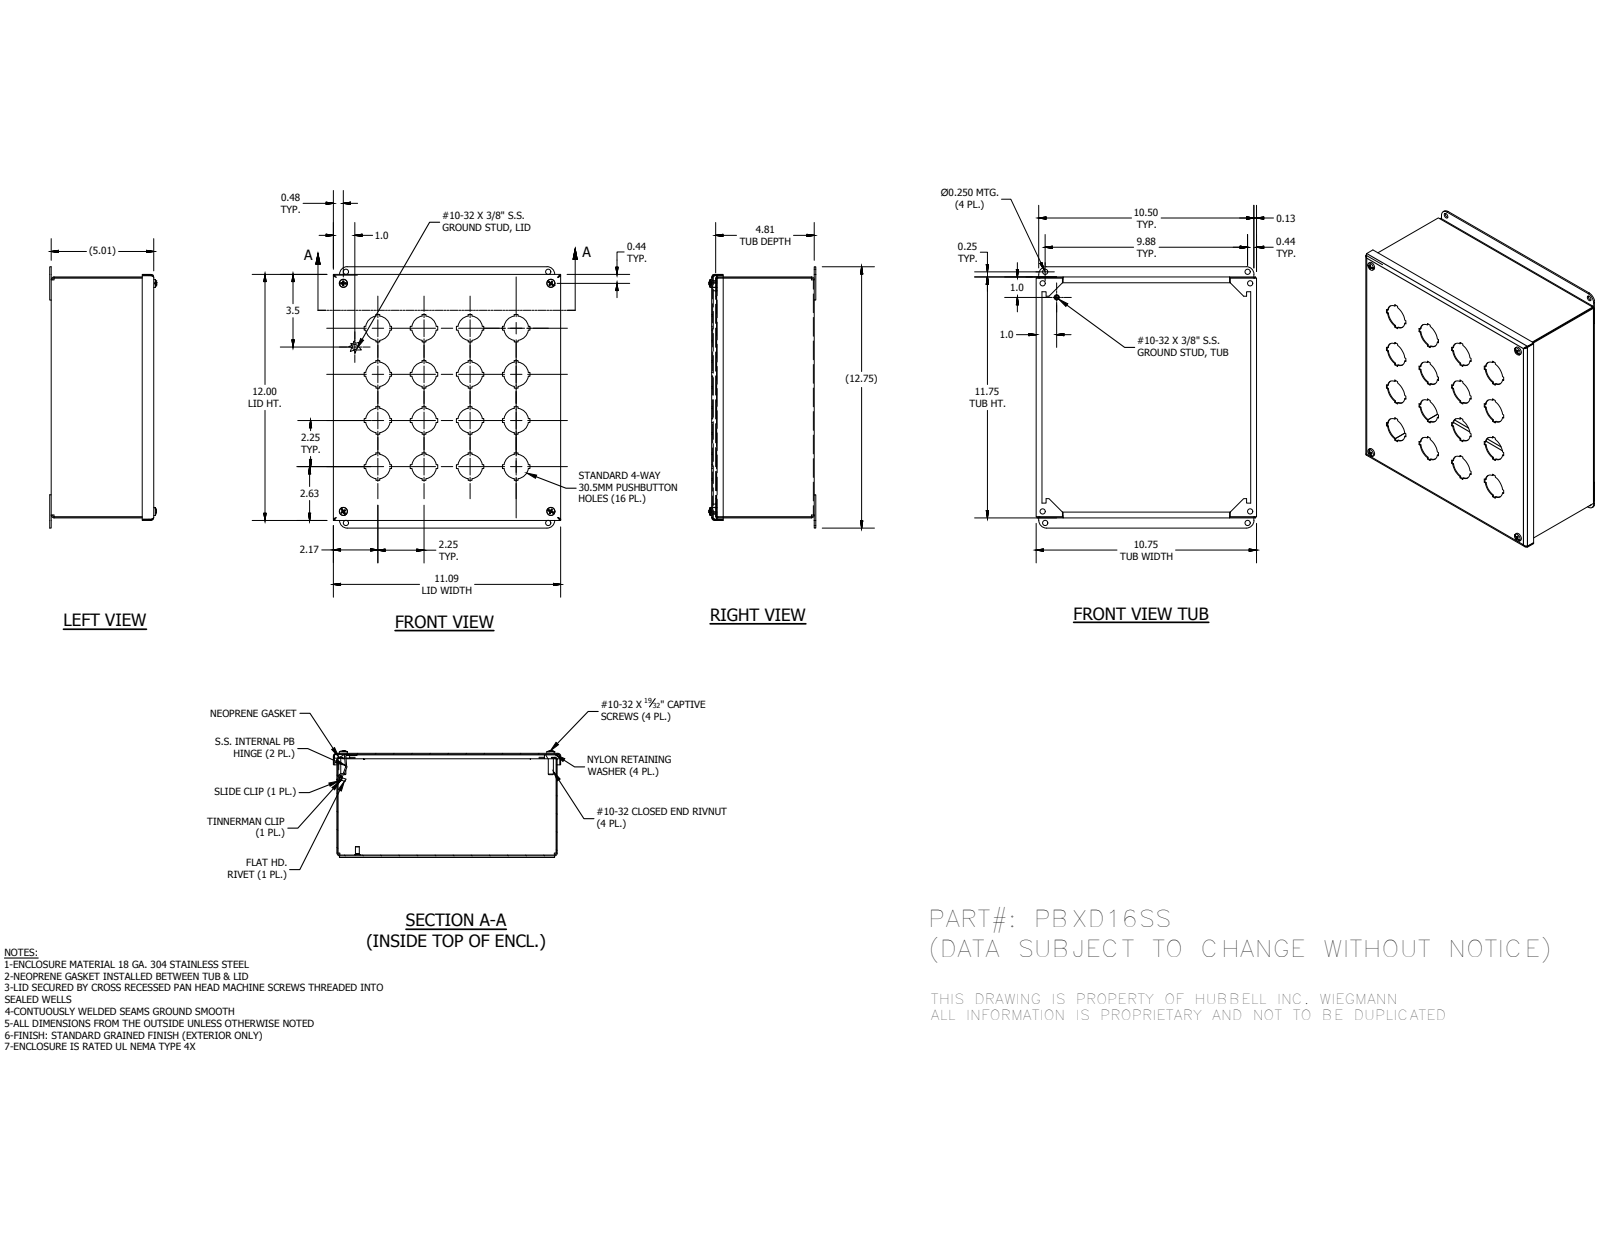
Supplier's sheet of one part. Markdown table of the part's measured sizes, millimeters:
| quantity | value |
| --- | --- |
| part name | PBXD16SSLID; 37210; 39077; PBXD16SSBKP (+8 more) |
| STEP written by | Autodesk Inventor 2016 (AUTOMOTIVE_DESIGN) |
| units | millimeters |
| bodies | 25 solids, 905 faces (601 planar, 196 cylindrical, 108 other) |
| overall size | 323.85 × 281.78 × 132.09 |
| volume | 504 523 mm³ |
| surface area | 740 923 mm² |
| round holes (diameter × count) | 30.48 × 16, 3.96 × 4, 4.98 × 4, 6.35 × 4, 6.53 × 4, 7.06 × 4, 7.14 × 4, 7.94 × 4, 3.38 × 2, 3.56 × 2 |
| round bosses / shafts (diameter × count) | 11.51 × 4, 10.31 × 4, 6.3 × 4, 4.25 × 4, 6.35 × 3, 4.83 × 2, 3.17 × 1 |
| partial cylindrical surfaces (radius × count) | 2.38 × 8, 3.52 × 8, 4.78 × 6, 1.59 × 4, 2.27 × 4, 2.29 × 4, 9.53 × 4, 0.8 × 3 |
| main face-to-face distances | 1.14, 1.15, 125.99, 124.84, 125.98, 127.13, 297.31, 271.9, 271.91, 273.05 |
| hole center spacings | 57.15, 127.79, 80.82, 114.3, 180.72, 161.64, 171.45, 206.06 |
